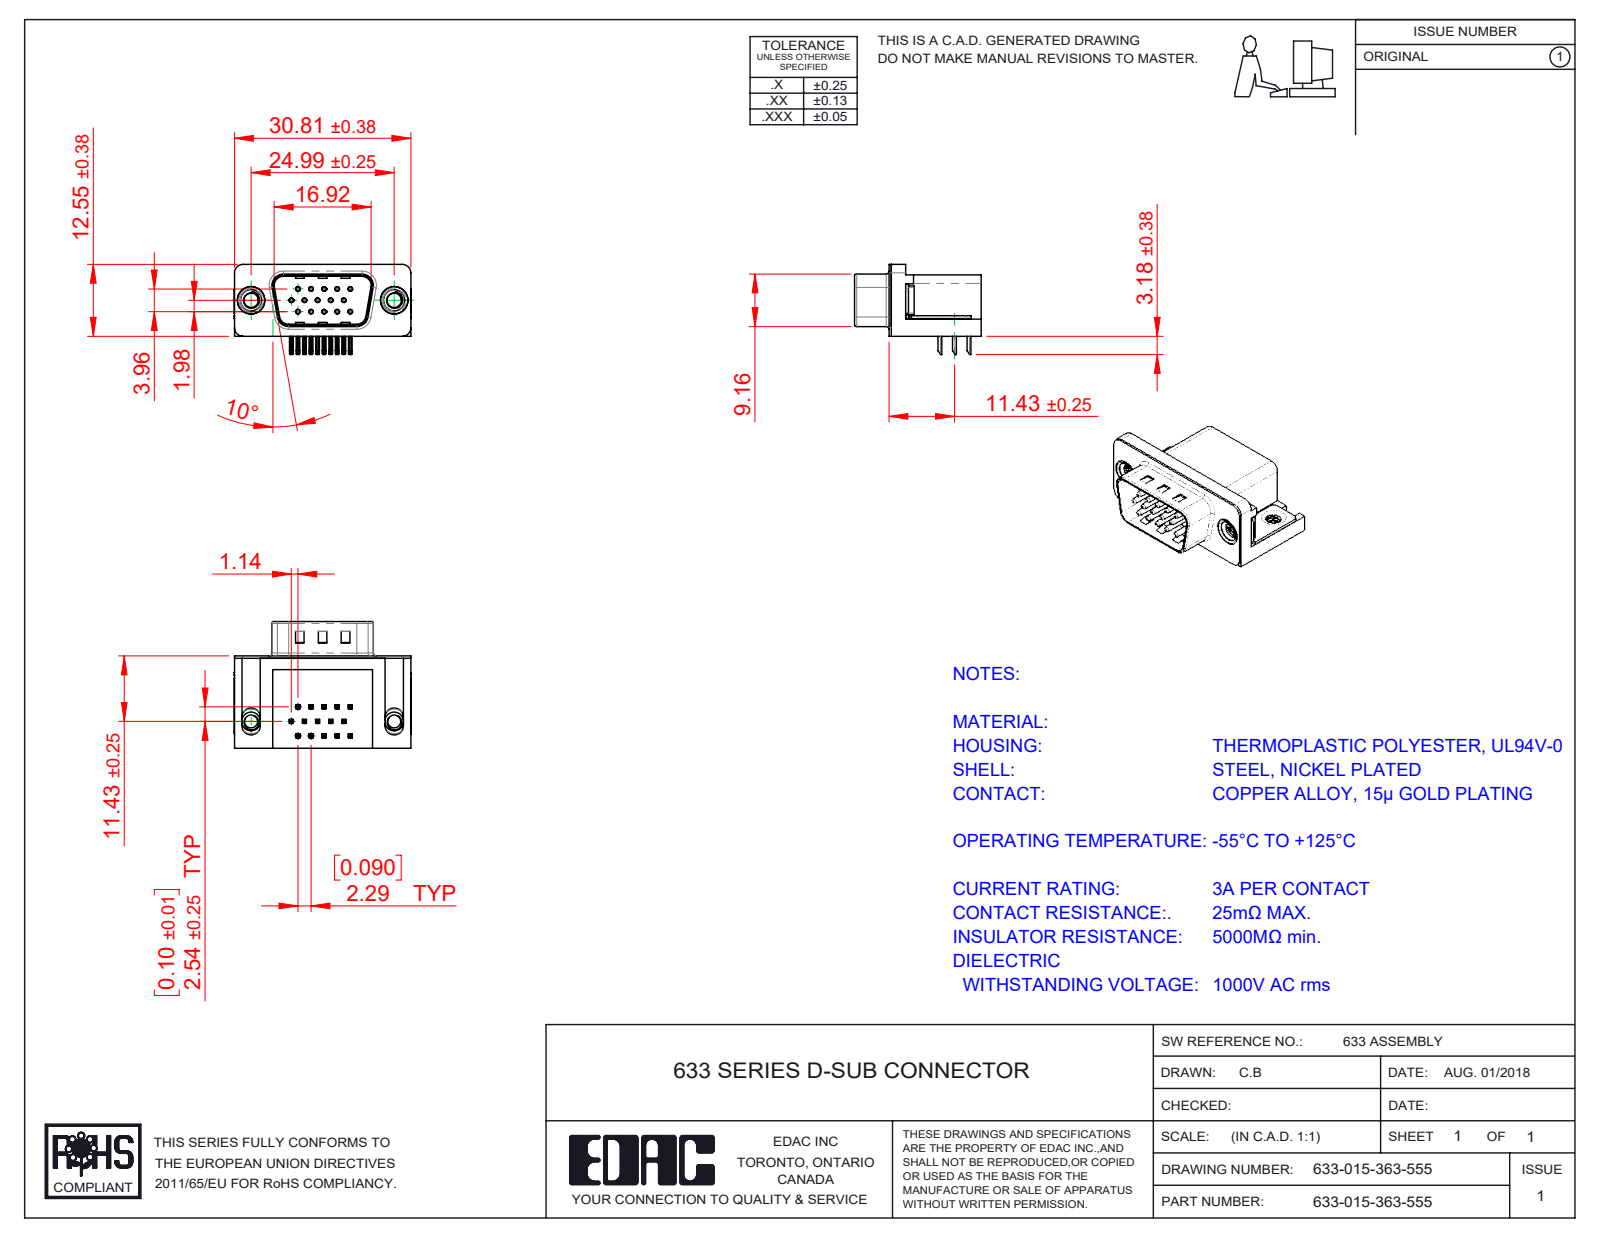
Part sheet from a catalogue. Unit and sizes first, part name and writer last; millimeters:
Units: millimetres
Overall size (bounding box): 30.89 × 22.1 × 15.73
Round holes (diameter × count): ⌀0.35 ×15, ⌀0.8 ×15, ⌀2.26 ×2, ⌀2.5 ×2, ⌀4 ×2, ⌀4.8 ×2, ⌀5 ×2
Round bosses / shafts (diameter × count): ⌀0.75 ×15, ⌀4.9 ×2, ⌀4.75 ×2, ⌀3.9 ×2, ⌀3.26 ×2
Partial cylindrical surfaces — rounded edges, fillets, slot ends (radius × count): R0.25 ×68, R0.12 ×30, R1 ×16, R0.5 ×9, R1.6 ×8, R1.5 ×7, R0.9 ×4, R2 ×4
Main face-to-face distances: 0.4, 10.35, 15.7, 2.9, 6.7, 16.1, 2.5, 0.5, 0.35, 10.7
Hole centre spacings: 3.96, 2.28, 4.57, 2.29, 6.05, 6.86, 7.92, 6.04
Volume: 4 080 mm³ · Surface area: 5 508 mm²
Bodies: 21 solids, 1473 faces (861 planar, 459 cylindrical, 153 other)
Part name (STEP PRODUCT): 633 Contact Top; 633 Shell_15 Contact; 633 Housing_15 Contact; 633 Contact Middle (+4 more)
STEP written by: SolidWorks 2016 (CONFIG_CONTROL_DESIGN)
